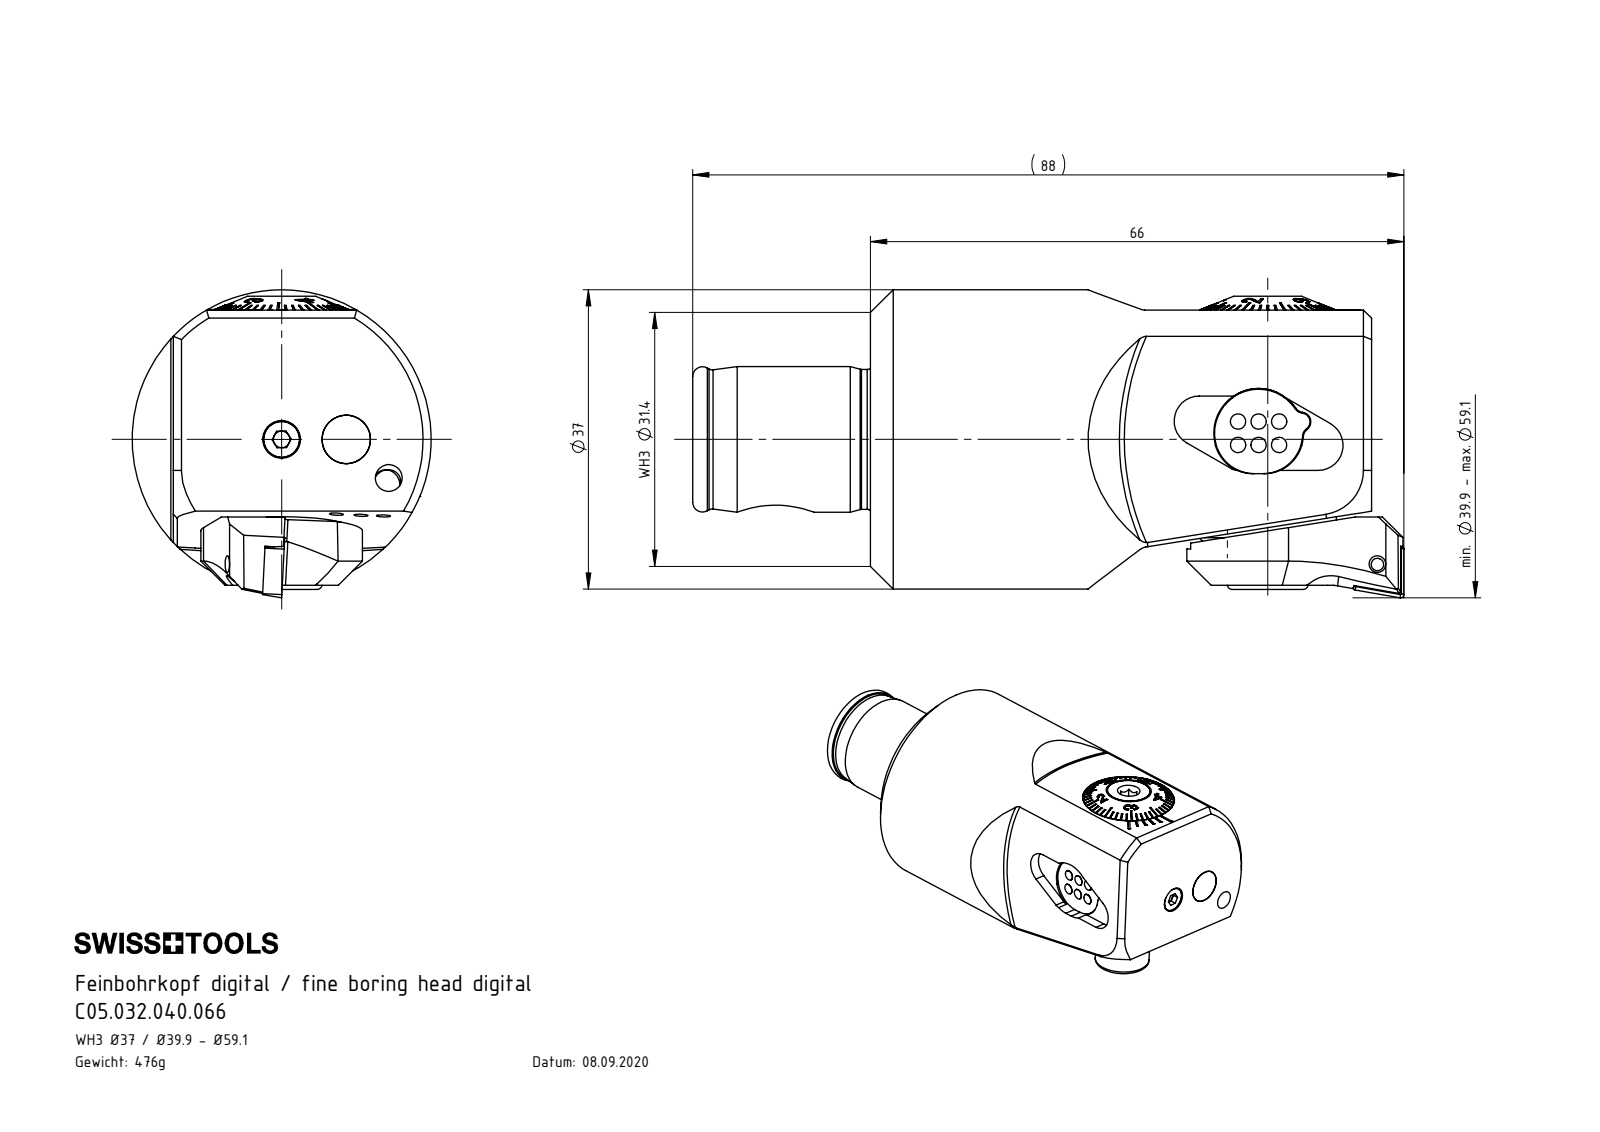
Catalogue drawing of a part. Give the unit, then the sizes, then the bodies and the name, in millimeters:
Units: millimetres
Overall size (bounding box): 84 × 37.05 × 37
Round holes (diameter × count): ⌀1.5 ×3, ⌀3.3 ×2, ⌀5 ×2, ⌀2.05 ×1, ⌀2.7 ×1, ⌀2.9 ×1, ⌀3 ×1, ⌀4.2 ×1, ⌀6 ×1, ⌀6.8 ×1, ⌀7 ×1, ⌀7.4 ×1
Round bosses / shafts (diameter × count): ⌀1.9 ×6, ⌀6 ×2, ⌀37 ×1, ⌀18 ×1, ⌀17.3 ×1, ⌀17 ×1, ⌀16.98 ×1, ⌀16.85 ×1
Partial cylindrical surfaces — rounded edges, fillets, slot ends (radius × count): R1.4 ×4, R0.5 ×3, R1.1 ×3, R1.2 ×3, R1.75 ×2, R2 ×2, R3.1 ×2, R4.8 ×2
Main face-to-face distances: 62, 4.5, 0.8, 3.7, 1.5, 6.75, 24.05, 2.2, 2.3, 28.55
Hole centre spacings: 1.52, 8, 8.72, 10.24
Volume: 59 980 mm³ · Surface area: 20 077 mm²
Bodies: 15 solids, 806 faces (401 planar, 143 cylindrical, 262 other)
Part name (STEP PRODUCT): DIN 3771 - 15x1.0; DIN 7984 - M6 x 10; T7 M2.5 x 6; ISO 4026 - M6 x 8 (+8 more)
STEP written by: SolidWorks 2017 (CONFIG_CONTROL_DESIGN)
